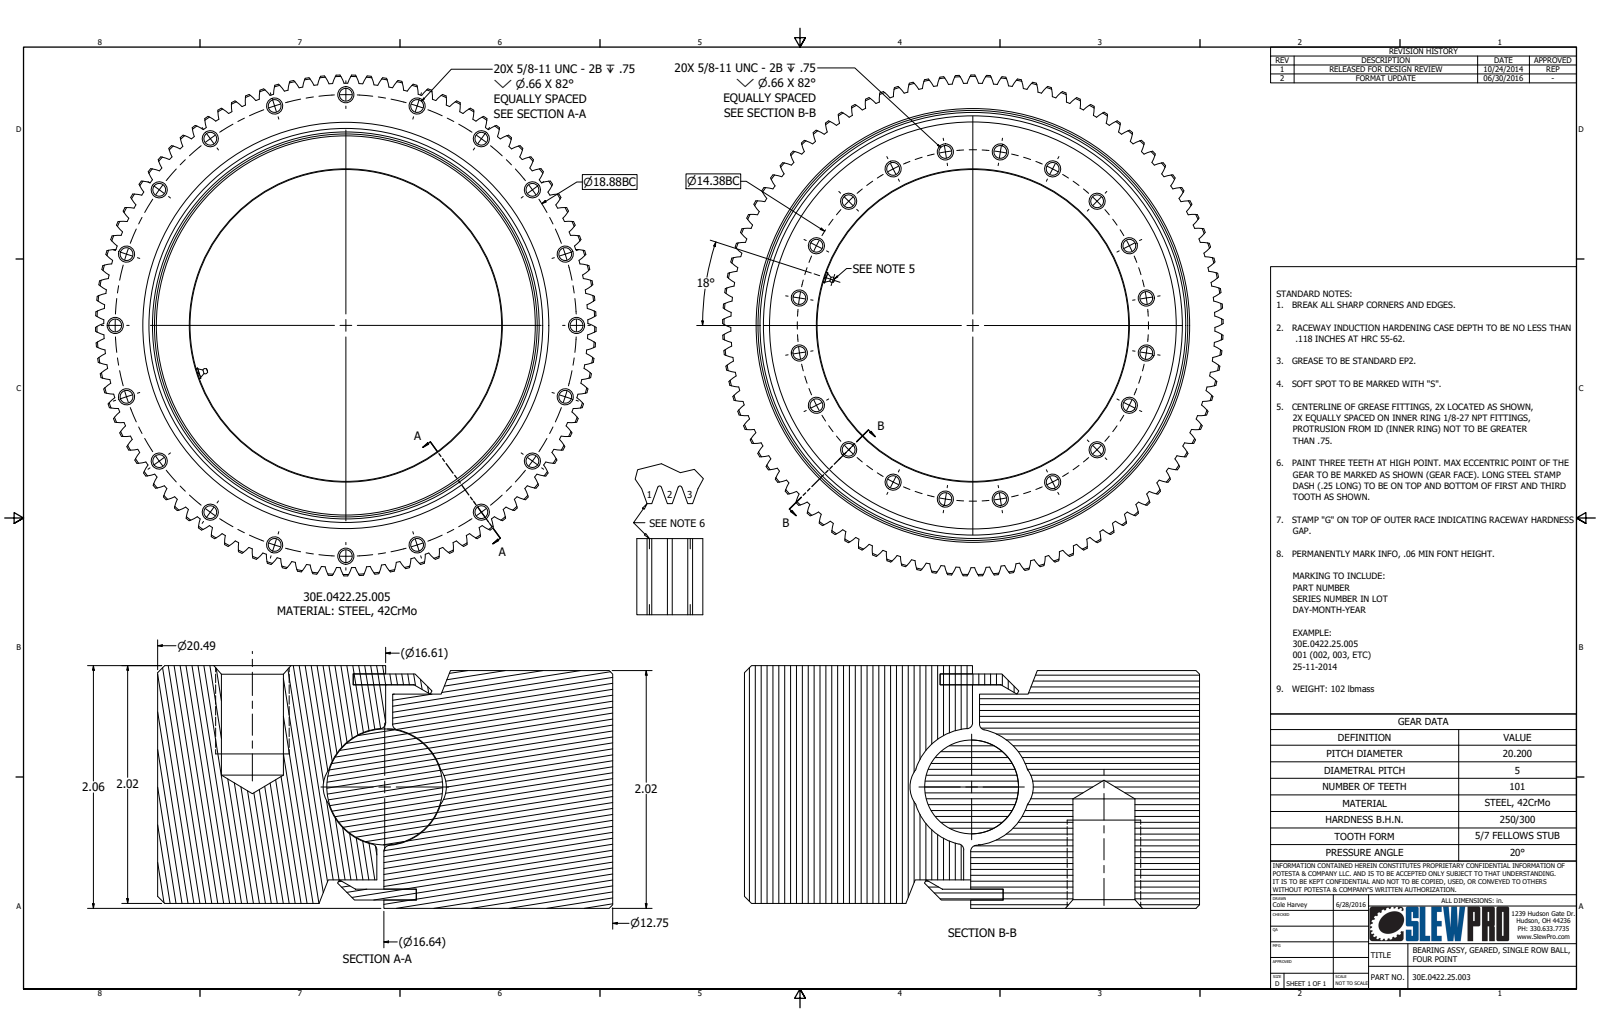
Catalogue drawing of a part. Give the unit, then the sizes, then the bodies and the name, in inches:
Units: inches
Overall size (bounding box): 20.485 × 20.483 × 2.062
Round holes (diameter × count): ⌀0.527 ×40, ⌀0.1 ×1, ⌀1.111 ×1, ⌀12.75 ×1, ⌀16.09 ×1, ⌀16.61 ×1, ⌀16.76 ×1, ⌀17.161 ×1
Round bosses / shafts (diameter × count): ⌀17.16 ×1, ⌀16.64 ×1, ⌀16.49 ×1, ⌀16.089 ×1, ⌀1.109 ×1
Partial cylindrical surfaces — rounded edges, fillets, slot ends (radius × count): R1.869 ×202, R9.906 ×1, R10.243 ×1
Main face-to-face distances: 0.042, 2.02, 1.828, 2.062, 1.978, 0.093, 0.071, 1.991, 0.029, 1.949
Hole centre spacings: 2.249, 4.442, 6.526, 7.187, 8.449, 10.165, 12.808, 14.198
Volume: 360.1 in³ · Surface area: 1 368 in²
Bodies: 6 solids, 939 faces (27 planar, 462 cylindrical, 450 other)
Part name (STEP PRODUCT): 30E.0422.25.003; Spur Gears1; 1_8 NPT Fitting
STEP written by: Autodesk Inventor 2026 (AUTOMOTIVE_DESIGN)
